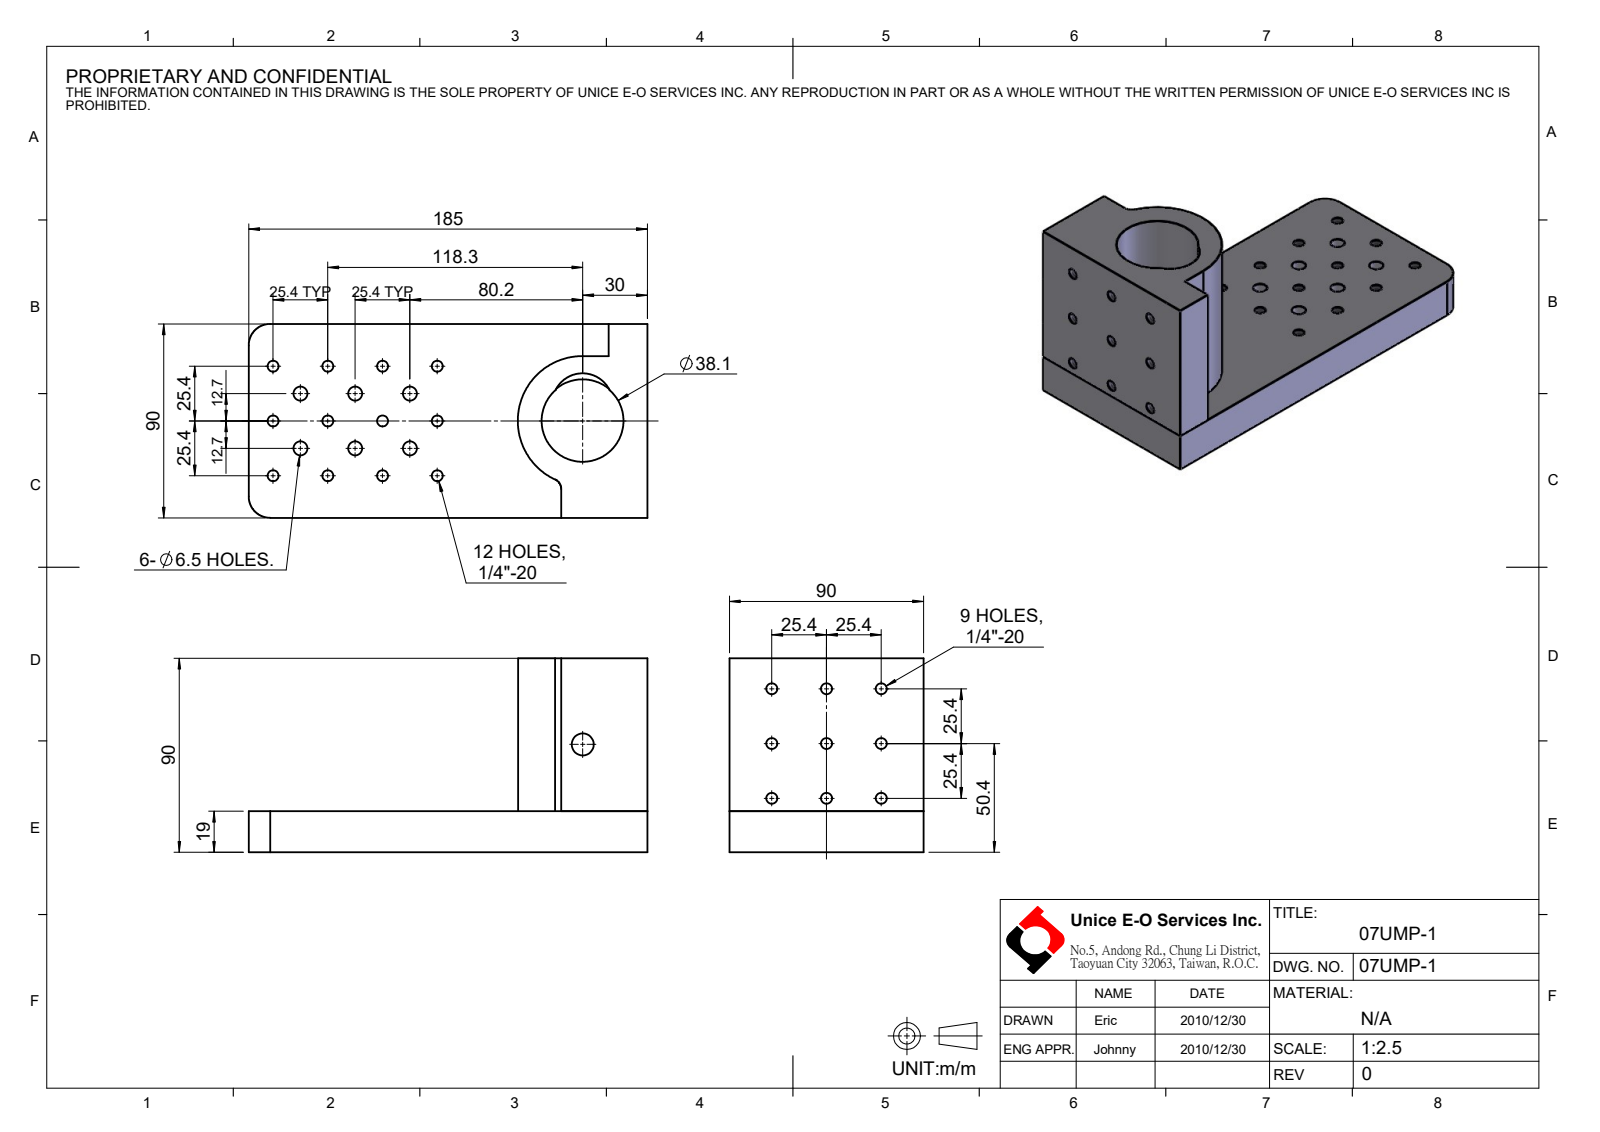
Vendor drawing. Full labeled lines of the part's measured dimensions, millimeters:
Part name (STEP PRODUCT): 07UMP-1
STEP written by: SolidWorks 2016 (CONFIG_CONTROL_DESIGN)
Units: millimetres
Bodies: 5 solids, 178 faces (47 planar, 95 cylindrical, 36 other)
Overall size (bounding box): 185 × 90 × 90
Volume: 485 467 mm³ · Surface area: 88 201 mm²
Round holes (diameter × count): ⌀5.11 ×21, ⌀6.5 ×6, ⌀4.2 ×3, ⌀5.5 ×3, ⌀10 ×3, ⌀10.2 ×1, ⌀38.5 ×1
Round bosses / shafts (diameter × count): ⌀8.5 ×3, ⌀5 ×3
Partial cylindrical surfaces — rounded edges, fillets, slot ends (radius × count): R10 ×2, R5 ×1, R14 ×1, R19.05 ×1, R30 ×1
Main face-to-face distances: 19, 90, 71, 185, 18, 167, 40, 145, 22, 15
Hole centre spacings: 25.4, 40.16, 17.96, 35.92, 56.8, 50.8, 53.88, 64.76
